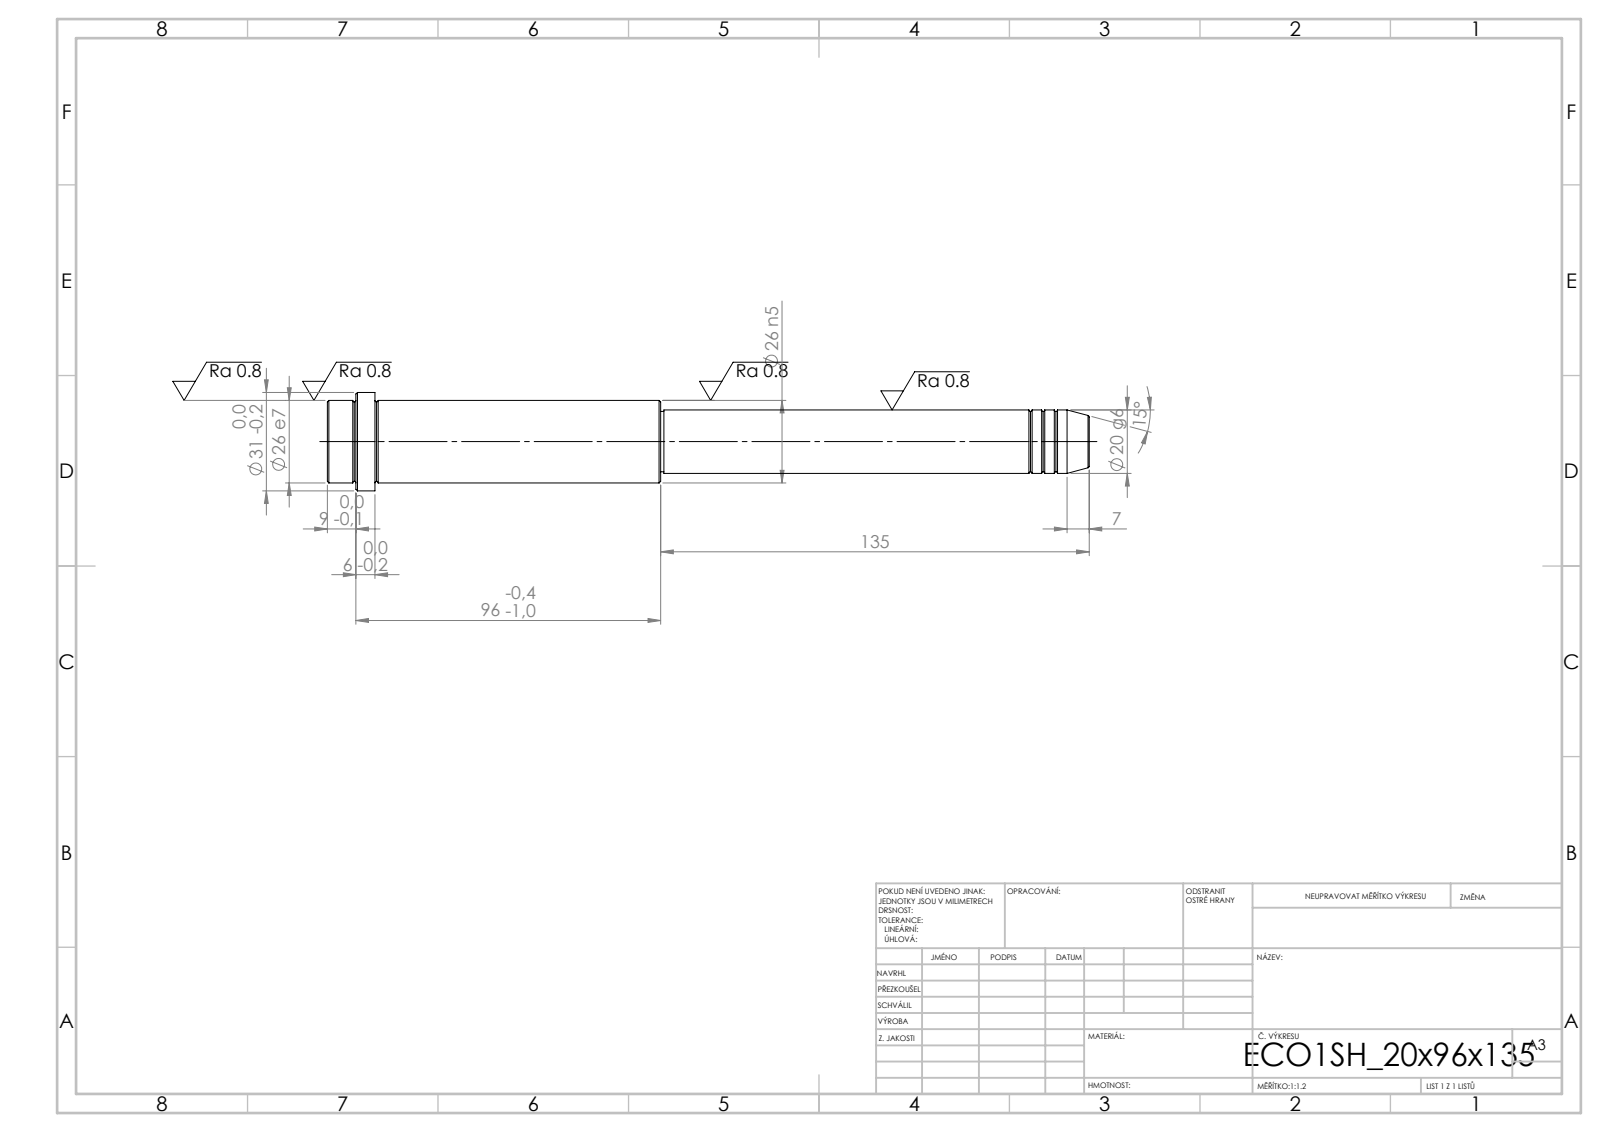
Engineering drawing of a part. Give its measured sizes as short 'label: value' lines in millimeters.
written by: SolidWorks 2019 (CONFIG_CONTROL_DESIGN)
unit: mm
bodies: 1 solid, 52 faces (6 planar, 16 cylindrical, 30 other)
size: 240 × 31 × 31
volume: 98 916 mm³; area: 18 689 mm²
bosses: 1× ⌀31, 1× ⌀26, 1× ⌀20, 1× ⌀19
face distances: 15, 90, 105, 135, 225, 240, 231, 96, 6, 9
